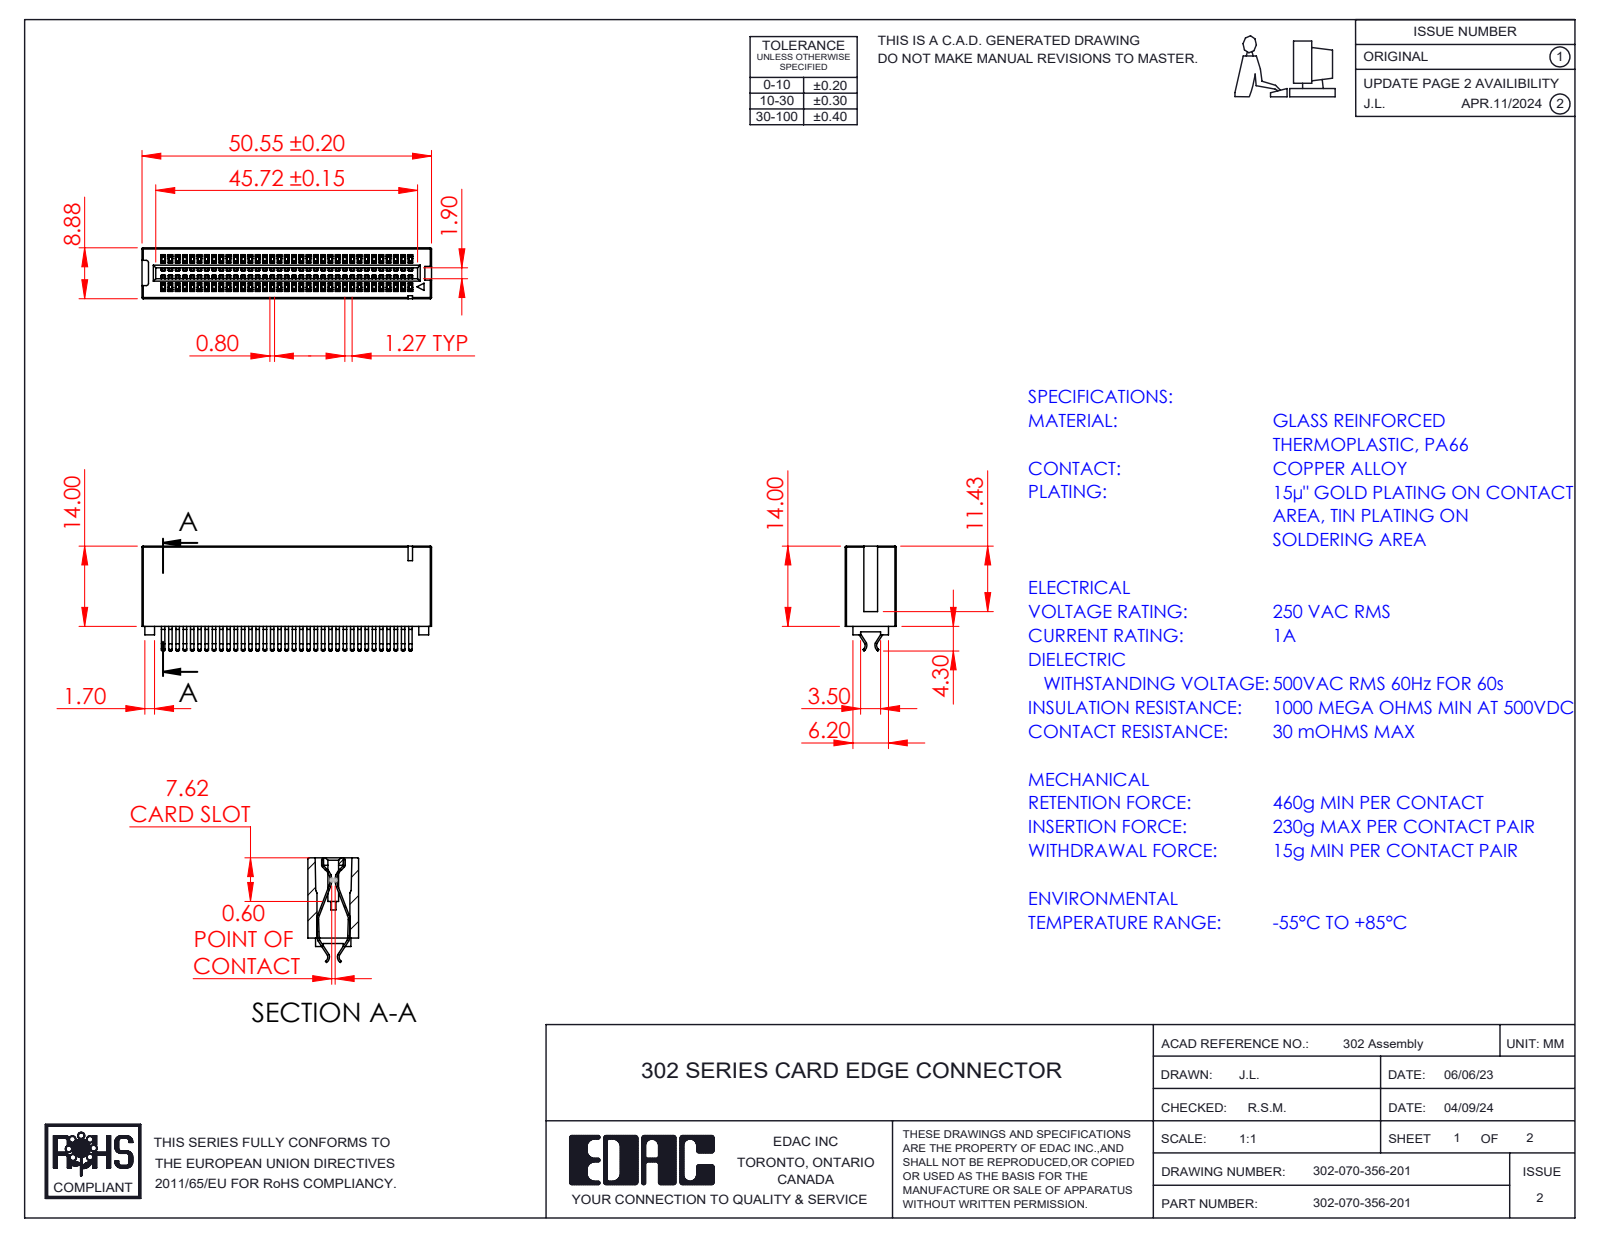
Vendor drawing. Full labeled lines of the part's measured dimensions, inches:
Part name (STEP PRODUCT): 302-070-356-201; HSG_Vertical HSG; Contact_302-290-X56
STEP written by: SolidWorks 2023 (CONFIG_CONTROL_DESIGN)
Units: inches
Bodies: 71 solids, 3391 faces (2254 planar, 1133 cylindrical, 4 other)
Overall size (bounding box): 1.99 × 0.72 × 0.35
Volume: 0.24 in³ · Surface area: 16.83 in²
Partial cylindrical surfaces — rounded edges, fillets, slot ends (radius × count): R0.008 ×218, R0.004 ×2, R0.016 ×2, R0.016 ×2, R0.037 ×2, R0.041 ×2, R0.048 ×2, R0.049 ×2
Main face-to-face distances: 0.05, 0.1, 0.15, 0.2, 0.25, 0.3, 0.35, 0.35, 0.4, 0.45
